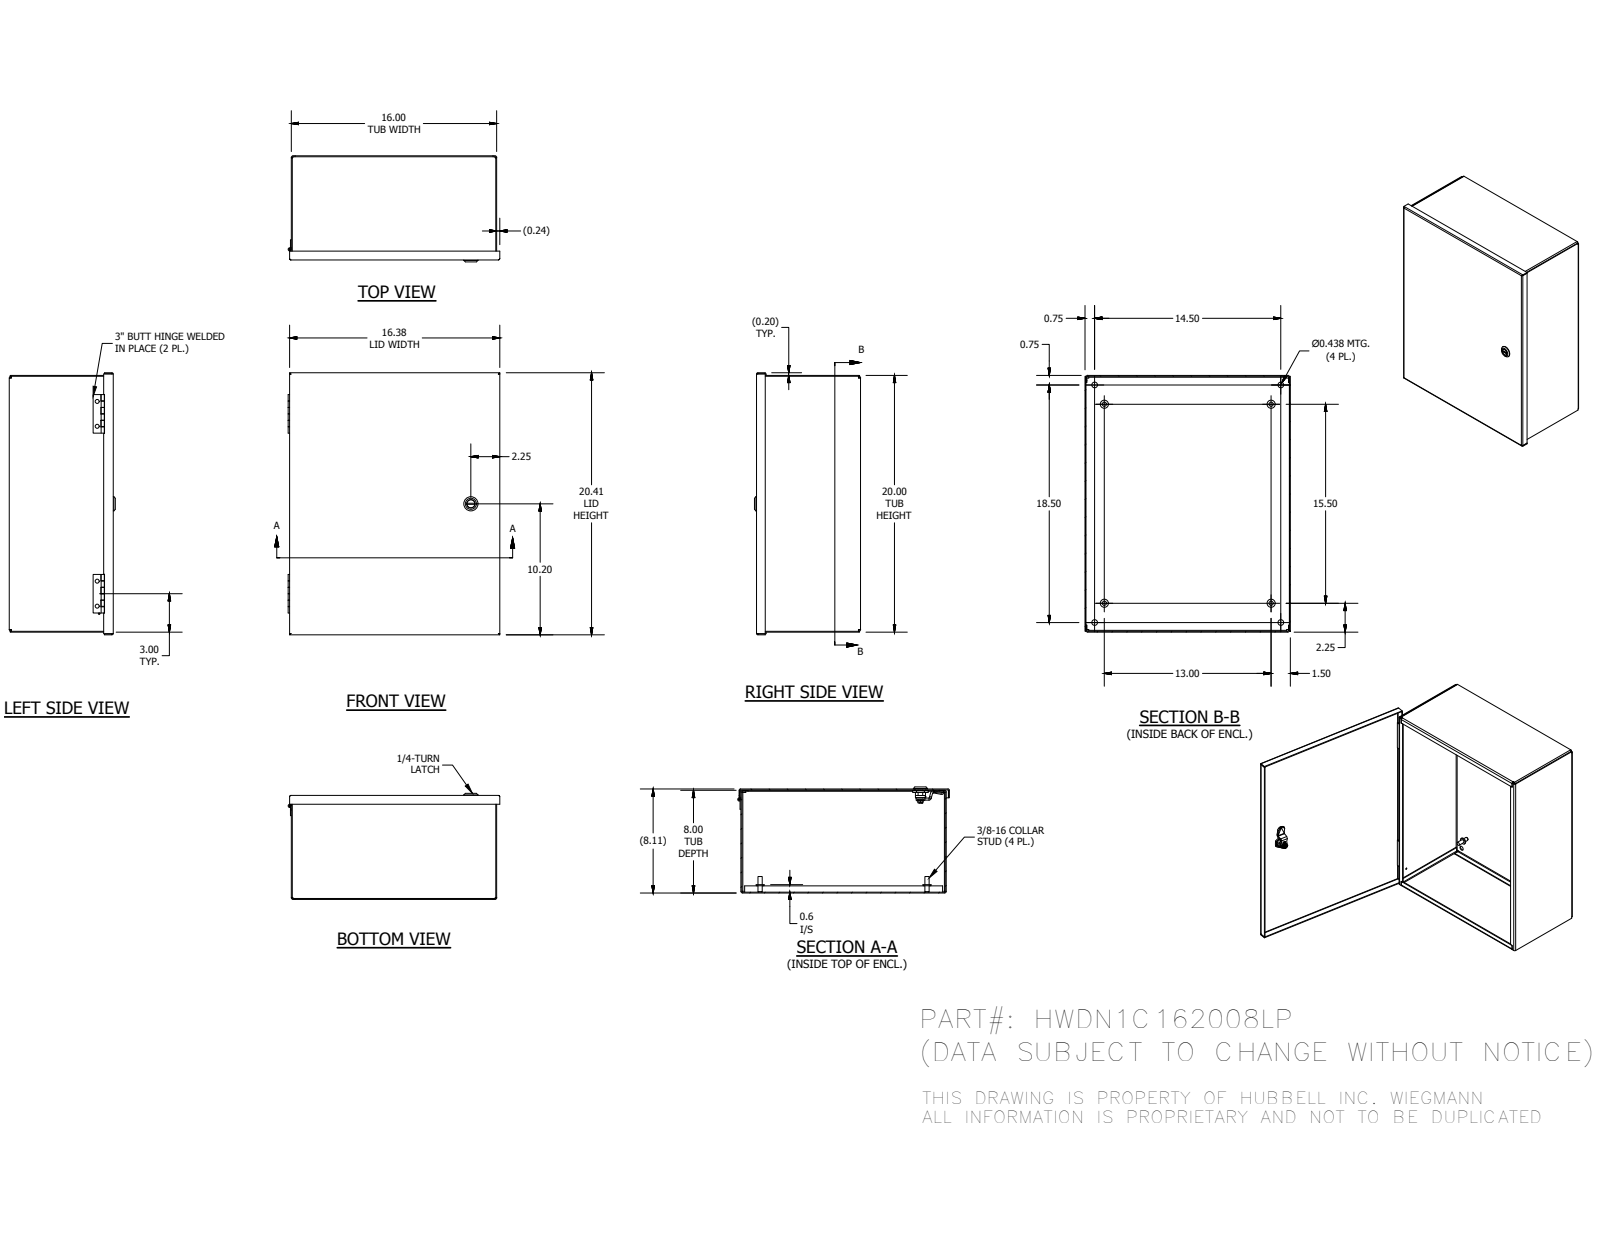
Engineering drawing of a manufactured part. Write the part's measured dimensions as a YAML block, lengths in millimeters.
part_name: "N1C162008LPBLR; N1C1608LPTB; N1C1620LPLID; 1000-101-GPF_GPD (+8 more)"
step_written_by: "Autodesk Inventor 2016 (AUTOMOTIVE_DESIGN)"
units: millimeters
bodies: {solids: 21, faces: 717, planar: 437, cylindrical: 212, other: 68}
overall_size: [518.32, 418.81, 228.92]
volume: 1696000
surface_area: 1816000
round_holes:
  - {diameter: 7.95, count: 4}
  - {diameter: 11.11, count: 4}
  - {diameter: 3.05, count: 1}
  - {diameter: 3.3, count: 1}
  - {diameter: 5, count: 1}
  - {diameter: 8, count: 1}
  - {diameter: 10, count: 1}
  - {diameter: 10.2, count: 1}
  - {diameter: 16.1, count: 1}
  - {diameter: 20.38, count: 1}
round_bosses_or_shafts:
  - {diameter: 15.88, count: 4}
  - {diameter: 8.38, count: 4}
  - {diameter: 28, count: 1}
  - {diameter: 27, count: 1}
  - {diameter: 23, count: 1}
  - {diameter: 19.8, count: 1}
  - {diameter: 15.8, count: 1}
  - {diameter: 15.2, count: 1}
partial_cylinders:
  - {radius: 0.3, count: 30}
  - {radius: 1.59, count: 12}
  - {radius: 3.47, count: 12}
  - {radius: 0.5, count: 10}
  - {radius: 0.79, count: 4}
  - {radius: 2.67, count: 4}
  - {radius: 4, count: 4}
  - {radius: 0.4, count: 3}
face_to_face_distances: [1.88, 223.04, 404.52, 221.16, 224.92, 506.12, 402.64, 406.4, 504.24, 508]
hole_center_spacings: [49.28, 237.12, 355.6, 368.3, 410.21, 469.9, 597.04, 15.51]
